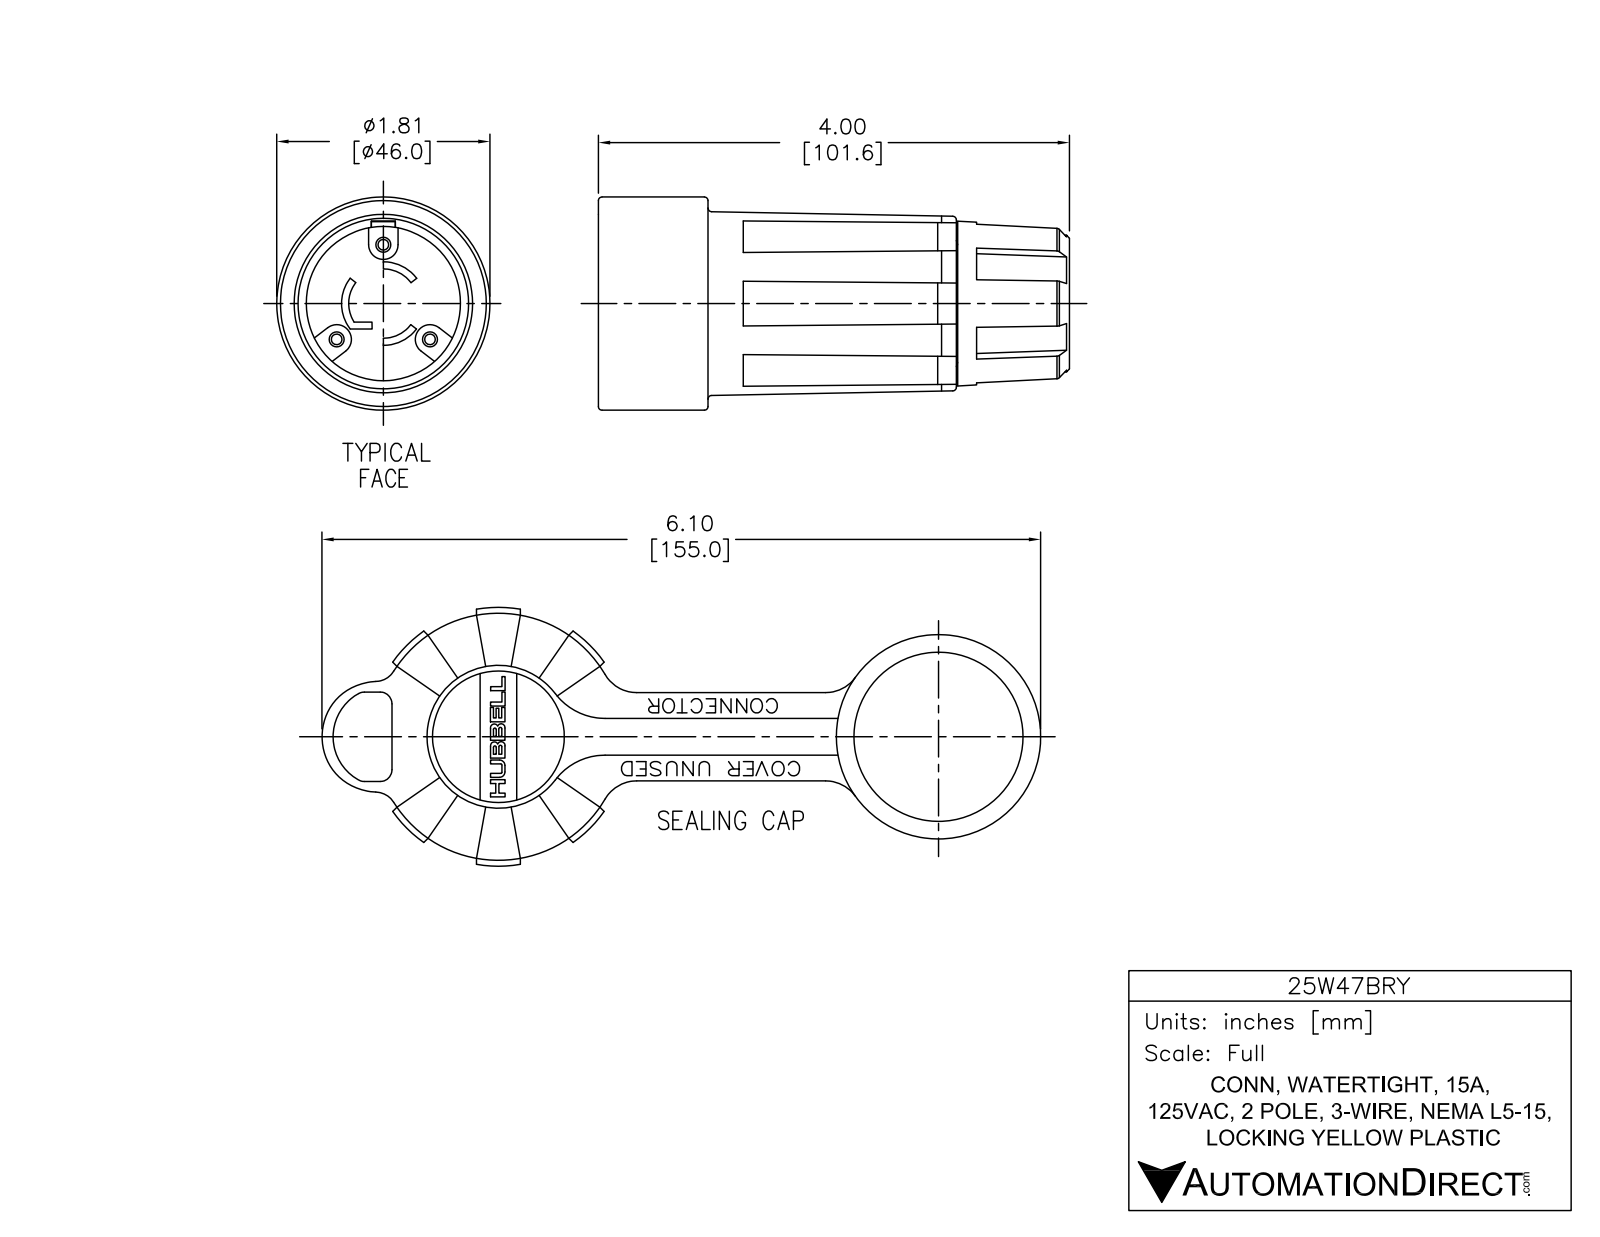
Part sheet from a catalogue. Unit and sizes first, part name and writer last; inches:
Units: inches
Overall size (bounding box): 6.2 × 4.105 × 2.2
Round holes (diameter × count): ⌀0.625 ×1, ⌀1.15 ×1, ⌀1.2 ×1, ⌀1.5 ×1, ⌀1.85 ×1
Round bosses / shafts (diameter × count): ⌀0.2 ×3, ⌀1.87 ×1, ⌀1.825 ×1, ⌀1.56 ×1, ⌀1.49 ×1, ⌀1.33 ×1, ⌀1 ×1
Partial cylindrical surfaces — rounded edges, fillets, slot ends (radius × count): R0.015 ×16, R0.25 ×4, R0.055 ×3, R0.11 ×3, R0.1 ×2, R0.12 ×2, R0.375 ×2, R0.3 ×1
Main face-to-face distances: 0.14, 0.06, 0.08, 0.45, 0.05, 0.615, 2.2, 2.06, 2.12, 0.165
Hole centre spacings: 3.8
Volume: 7.491 in³ · Surface area: 59.82 in²
Bodies: 1 solid, 330 faces (132 planar, 96 cylindrical, 102 other)
Part name (STEP PRODUCT): 25W47BRY
STEP written by: SolidWorks 2013 (AUTOMOTIVE_DESIGN)
